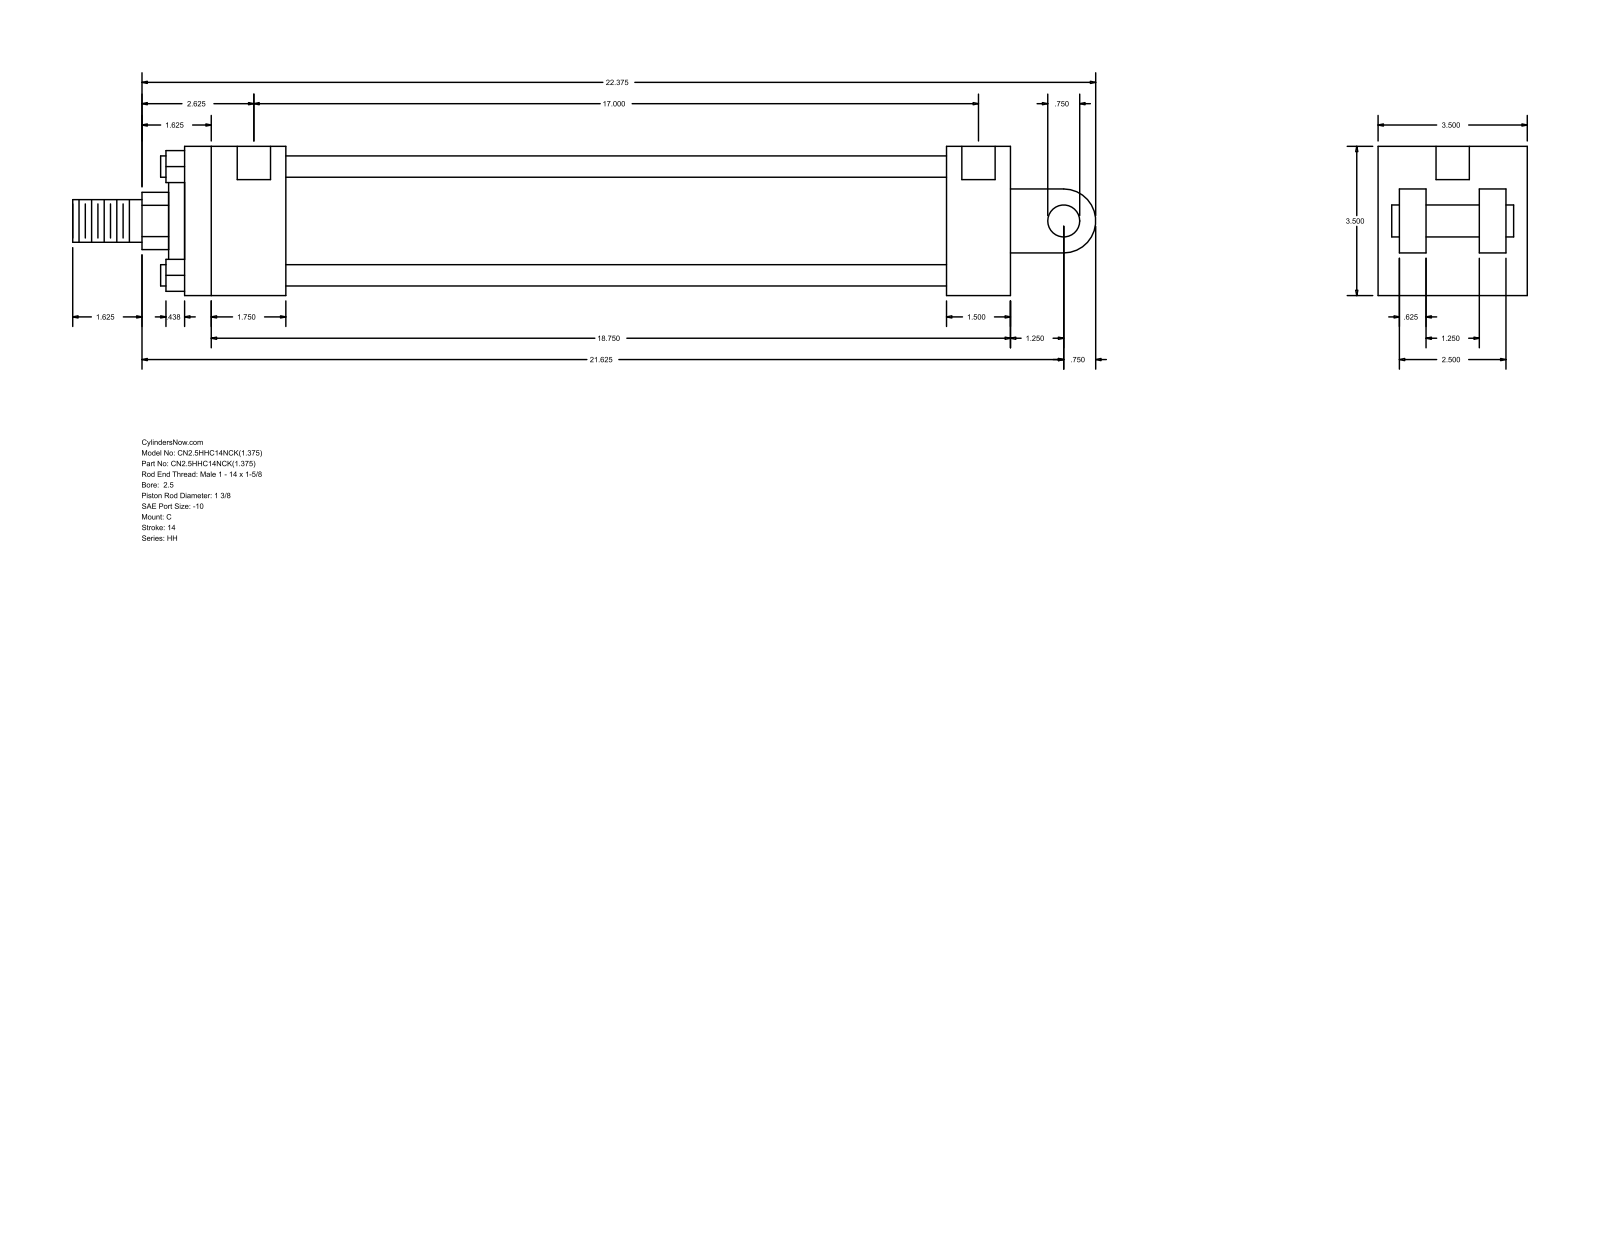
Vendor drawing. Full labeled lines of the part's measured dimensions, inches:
Part name (STEP PRODUCT): HH_C__0250_1.375
STEP written by: GSSL Pune (CONFIG_CONTROL_DESIGN)
Units: inches
Bodies: 0 solids, 99 faces (70 planar, 29 cylindrical, 0 other)
Overall size (bounding box): 24 × 3.5 × 3.5
Round holes (diameter × count): ⌀0.219 ×4, ⌀0.781 ×2
Round bosses / shafts (diameter × count): ⌀0.5 ×4, ⌀2.875 ×1, ⌀2 ×1, ⌀1.375 ×1, ⌀1 ×1, ⌀0.75 ×1
Partial cylindrical surfaces — rounded edges, fillets, slot ends (radius × count): R0.672 ×1, R0.75 ×1
Main face-to-face distances: 3.5, 19.375, 2.5, 0.5, 17.875, 1.5, 2.375, 15.5, 17, 1.125
Hole centre spacings: 0.062, 17.063, 17.125, 17
